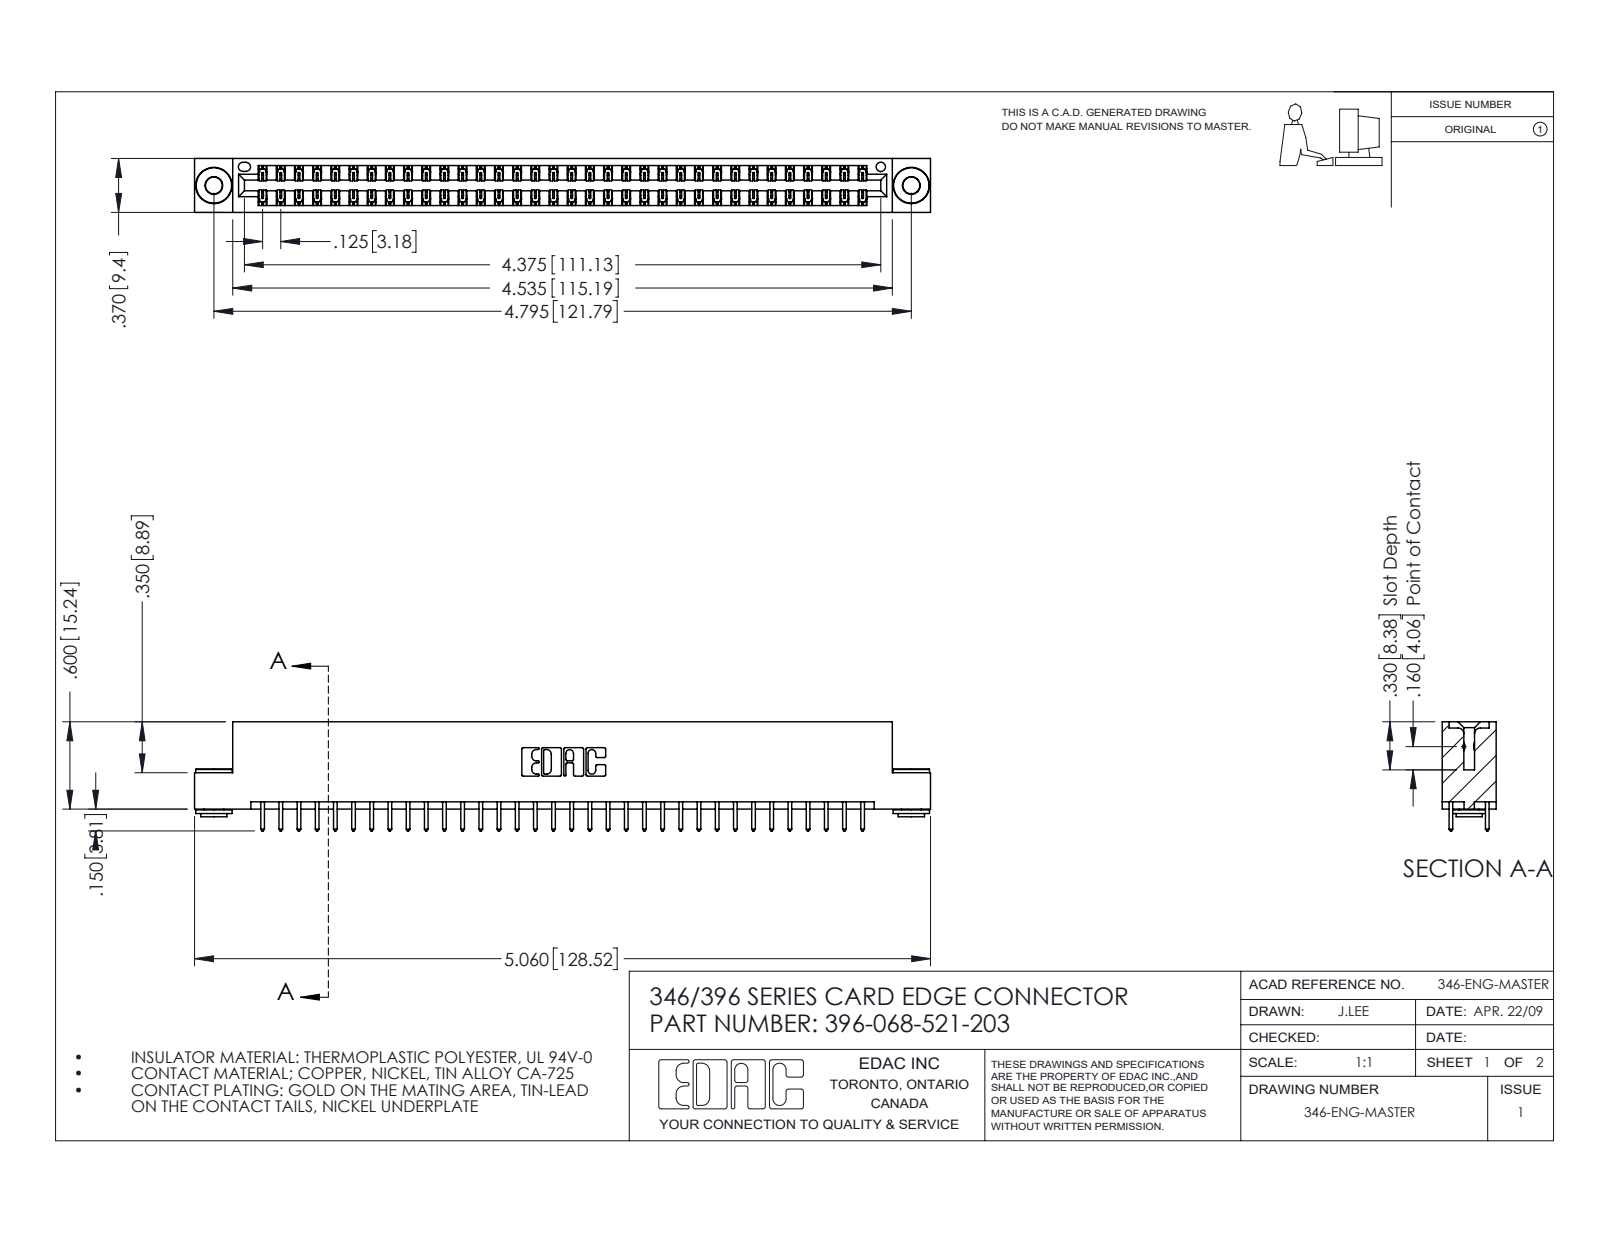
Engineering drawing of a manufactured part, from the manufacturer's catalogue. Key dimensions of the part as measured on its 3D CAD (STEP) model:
Part name (STEP PRODUCT): 346 Part_Flush Mounting Lugs - 0.156 Dia-TH; 396-068-521-203; 345-250-002_345-250-002-102; 345-292-001_345-293-121
STEP written by: SolidWorks 2016 (CONFIG_CONTROL_DESIGN)
Units: inches
Bodies: 71 solids, 3696 faces (2466 planar, 1222 cylindrical, 8 other)
Overall size (bounding box): 5.06 × 0.75 × 0.37
Volume: 0.76 in³ · Surface area: 26.4 in²
Round holes (diameter × count): ⌀0.116 ×2, ⌀0.156 ×2, ⌀0.064 ×1
Round bosses / shafts (diameter × count): ⌀0.25 ×2, ⌀0.18 ×2, ⌀0.136 ×2
Partial cylindrical surfaces — rounded edges, fillets, slot ends (radius × count): R0.006 ×102, R0.01 ×68, R0.01 ×22, R0.007 ×6, R0.031 ×6, R0.026 ×3, R0.014 ×2, R0.022 ×2
Main face-to-face distances: 0.048, 0.322, 0.25, 0.37, 0.025, 0.072, 0.298, 0.275, 0.148, 0.222
Hole centre spacings: 0.246, 4.587, 4.795
